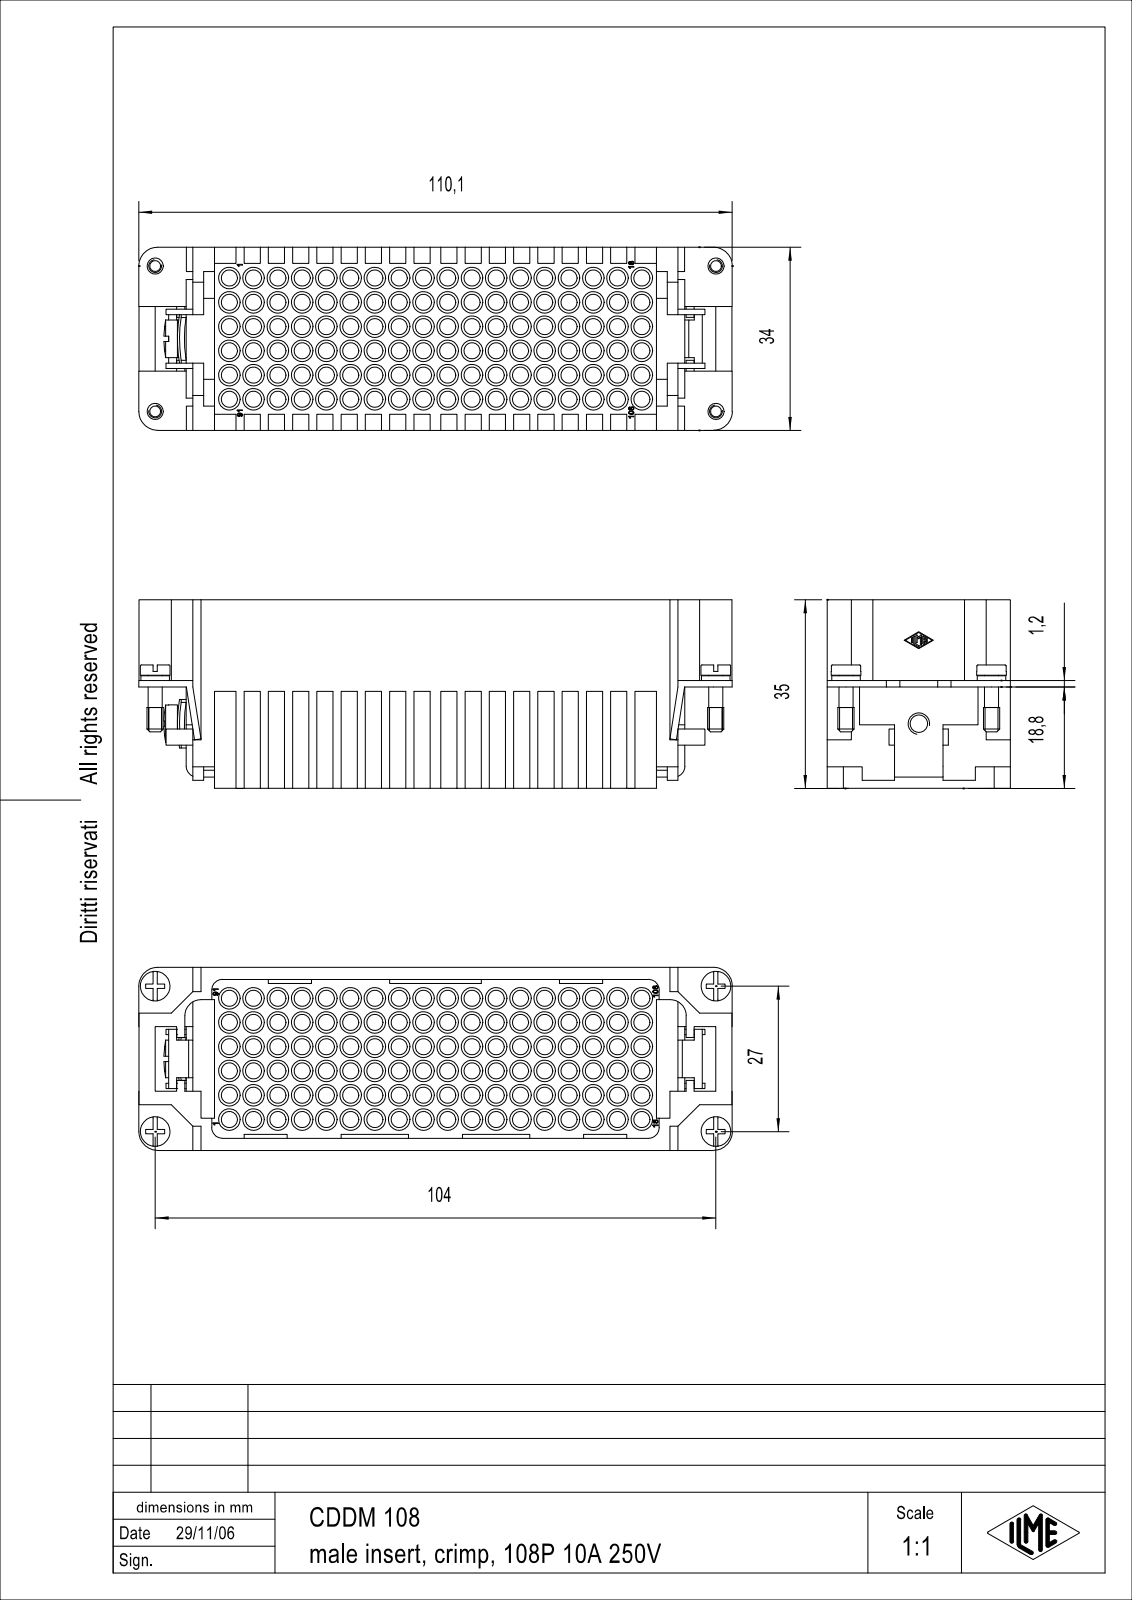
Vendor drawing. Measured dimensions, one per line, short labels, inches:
name: CDDM 108
written by: Autodesk Inventor 7 (AUTOMOTIVE_DESIGN)
unit: in
bodies: 1 solid, 1707 faces (627 planar, 710 cylindrical, 370 other)
size: 4.335 × 1.378 × 1.339
volume: 2.457 in³; area: 83.46 in²
holes: 108× ⌀0.118, 108× ⌀0.157, 1× ⌀0.128
bosses: 2× ⌀0.217, 2× ⌀0.209, 2× ⌀0.118, 2× ⌀0.102, 1× ⌀0.276
rounds: 14× R0.004, 8× R0.079, 2× R0.118, 2× R0.138, 1× R0.236
face distances: 0.118, 1.339, 1.22, 0.079, 0.669, 0.089, 0.03, 1.132, 0.098, 1.25
hole spacings: 0.177, 0.354, 0.531, 0.25, 0.396, 0.709, 0.56, 0.73
